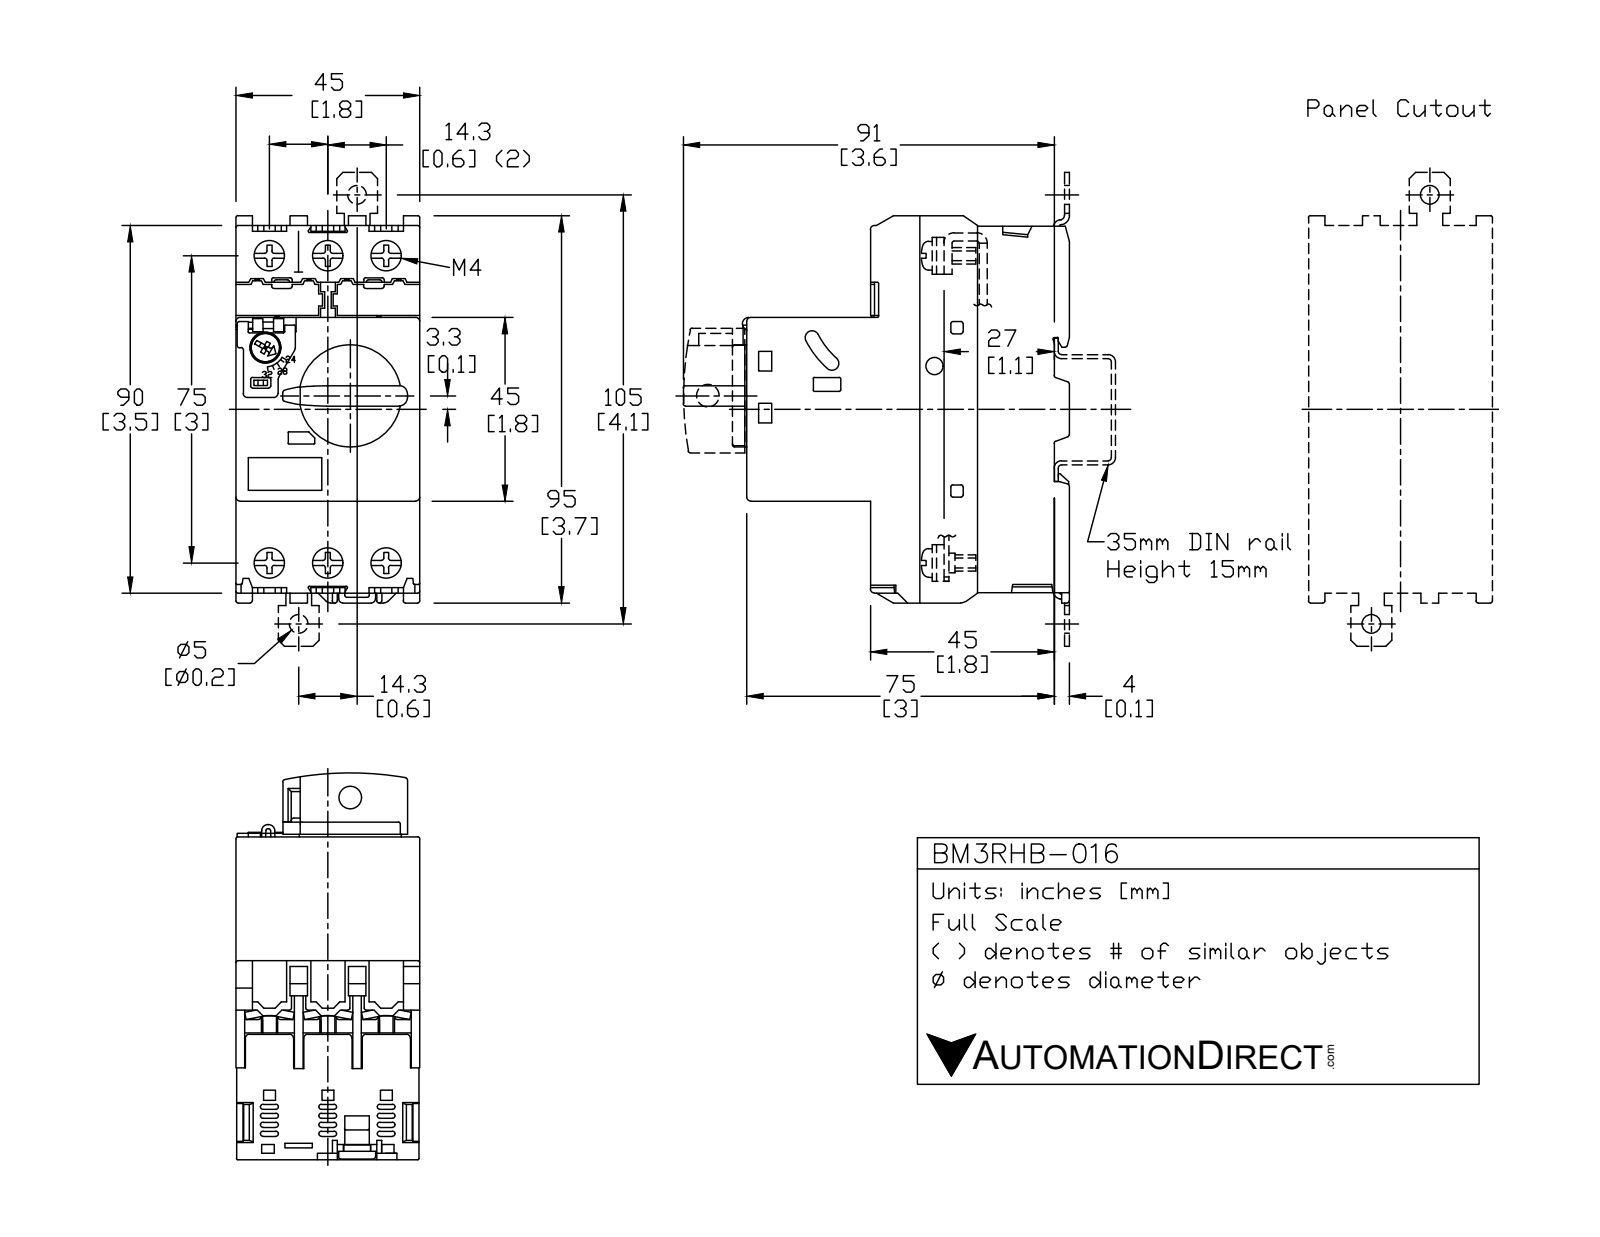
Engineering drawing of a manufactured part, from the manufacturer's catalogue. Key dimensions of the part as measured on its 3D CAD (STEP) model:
Part name (STEP PRODUCT): BM3RHB-016
STEP written by: SolidWorks 2018 (AUTOMOTIVE_DESIGN)
Units: inches
Bodies: 25 solids, 1294 faces (964 planar, 327 cylindrical, 3 other)
Overall size (bounding box): 3.732 × 3.72 × 1.772
Volume: 14.13 in³ · Surface area: 88.41 in²
Round holes (diameter × count): ⌀0.157 ×6, ⌀0.291 ×6, ⌀0.063 ×1, ⌀0.165 ×1, ⌀0.197 ×1, ⌀0.217 ×1, ⌀0.295 ×1
Round bosses / shafts (diameter × count): ⌀0.236 ×6, ⌀0.984 ×1, ⌀0.276 ×1
Partial cylindrical surfaces — rounded edges, fillets, slot ends (radius × count): R0.02 ×67, R0.024 ×24, R0.079 ×14, R0.012 ×12, R0.039 ×8, R0.098 ×8, R0.008 ×6, R0.059 ×2
Main face-to-face distances: 1.772, 1.441, 1.669, 3.11, 0.882, 2.654, 0.118, 0.65, 0.791, 0.472
Hole centre spacings: 0.563, 3.006, 2.953, 1.126, 3.16, 0.883, 0.941, 1.068
